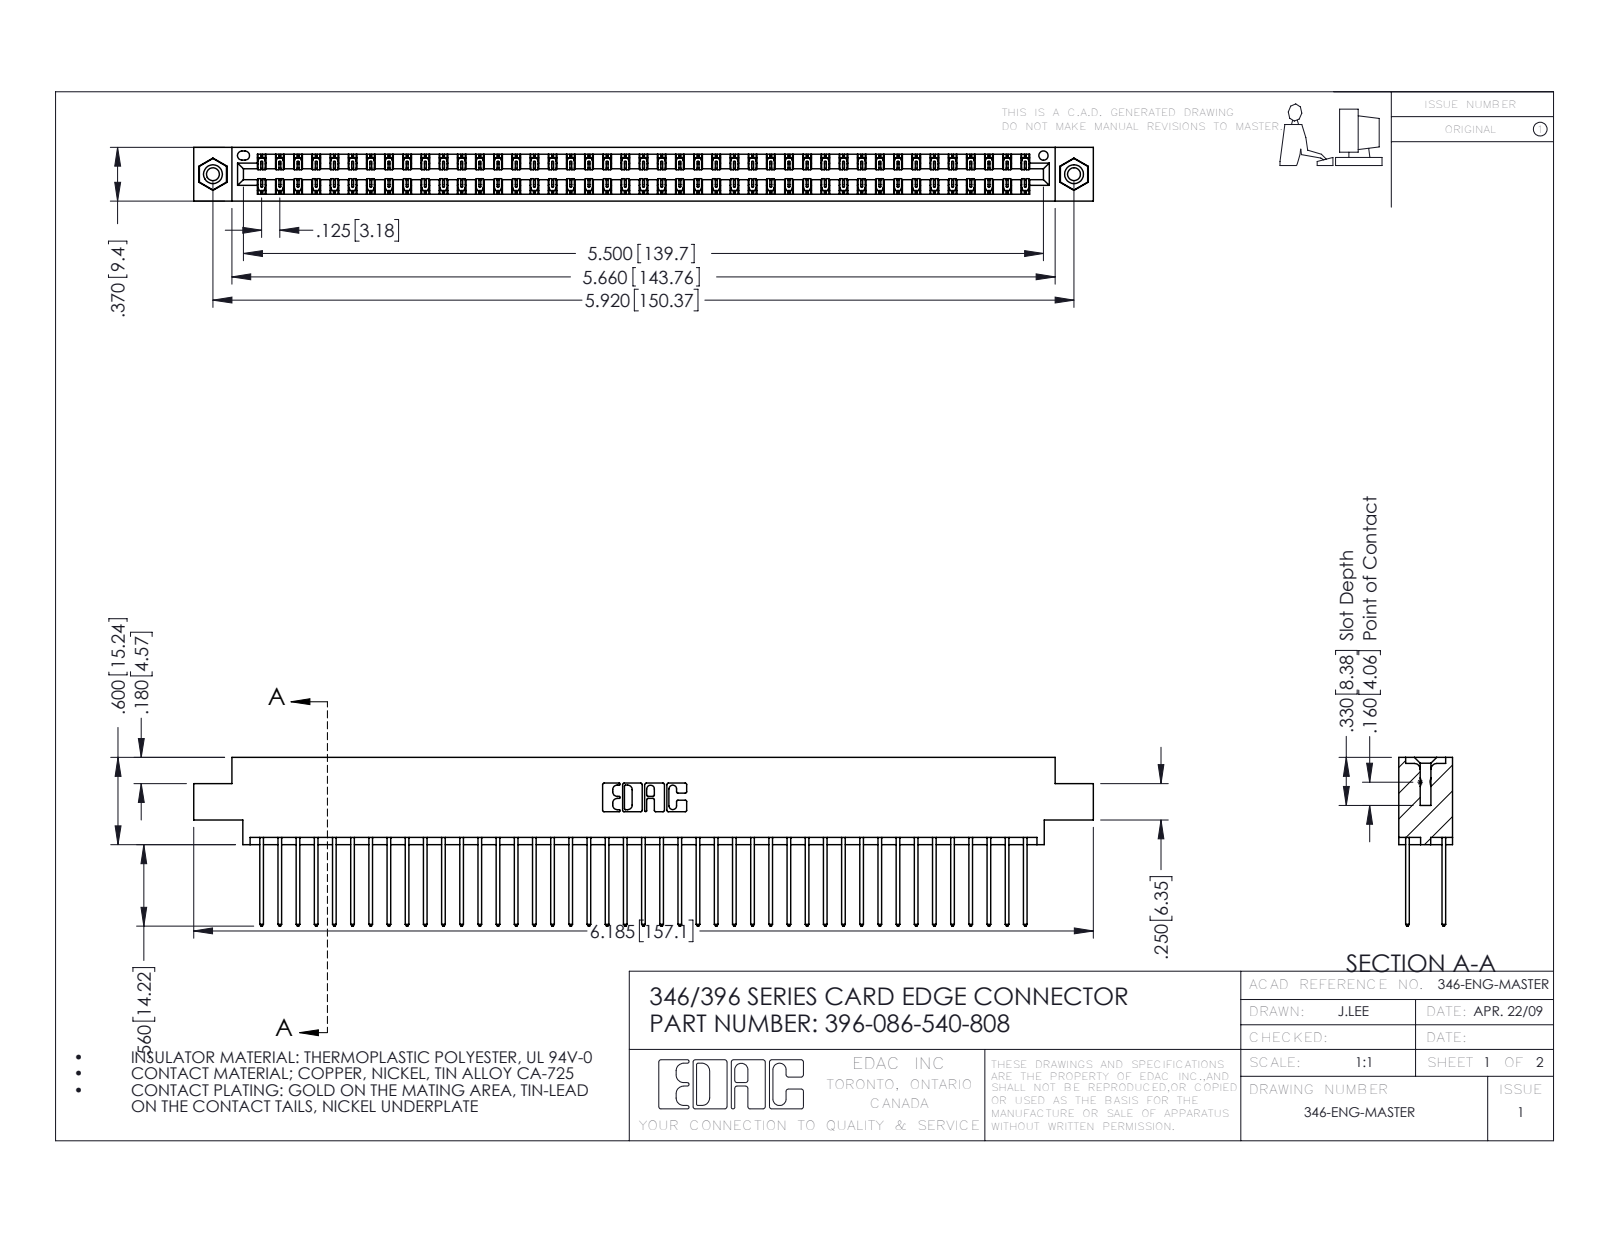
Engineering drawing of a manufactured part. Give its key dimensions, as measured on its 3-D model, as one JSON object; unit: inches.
{"part_name": "345-250-001_345-250-003-102; 396-086-540-808; 346 Part_0.170 Offset - 0.156 Dia-TI; 345-292-001_345-293-140", "step_written_by": "SolidWorks 2016 (CONFIG_CONTROL_DESIGN)", "units": "inches", "bodies": {"solids": 89, "faces": 4658, "planar": 3122, "cylindrical": 1520, "other": 16}, "overall_size": [6.185, 1.16, 0.37], "volume_in3": 0.945, "surface_area_in2": 35.73, "round_holes": [[0.089, 2], [0.125, 2], [0.156, 2], [0.064, 1]], "round_bosses_or_shafts": [[0.155, 2]], "partial_cylinders_radius": [[0.006, 129], [0.01, 86], [0.01, 22], [0.007, 6], [0.031, 6], [0.026, 3], [0.014, 2], [0.022, 2]], "face_to_face_distances": [0.048, 0.322, 0.25, 0.072, 0.298, 0.025, 0.37, 0.275, 0.222, 0.148], "hole_center_spacings": [0.246, 5.711, 5.92]}
